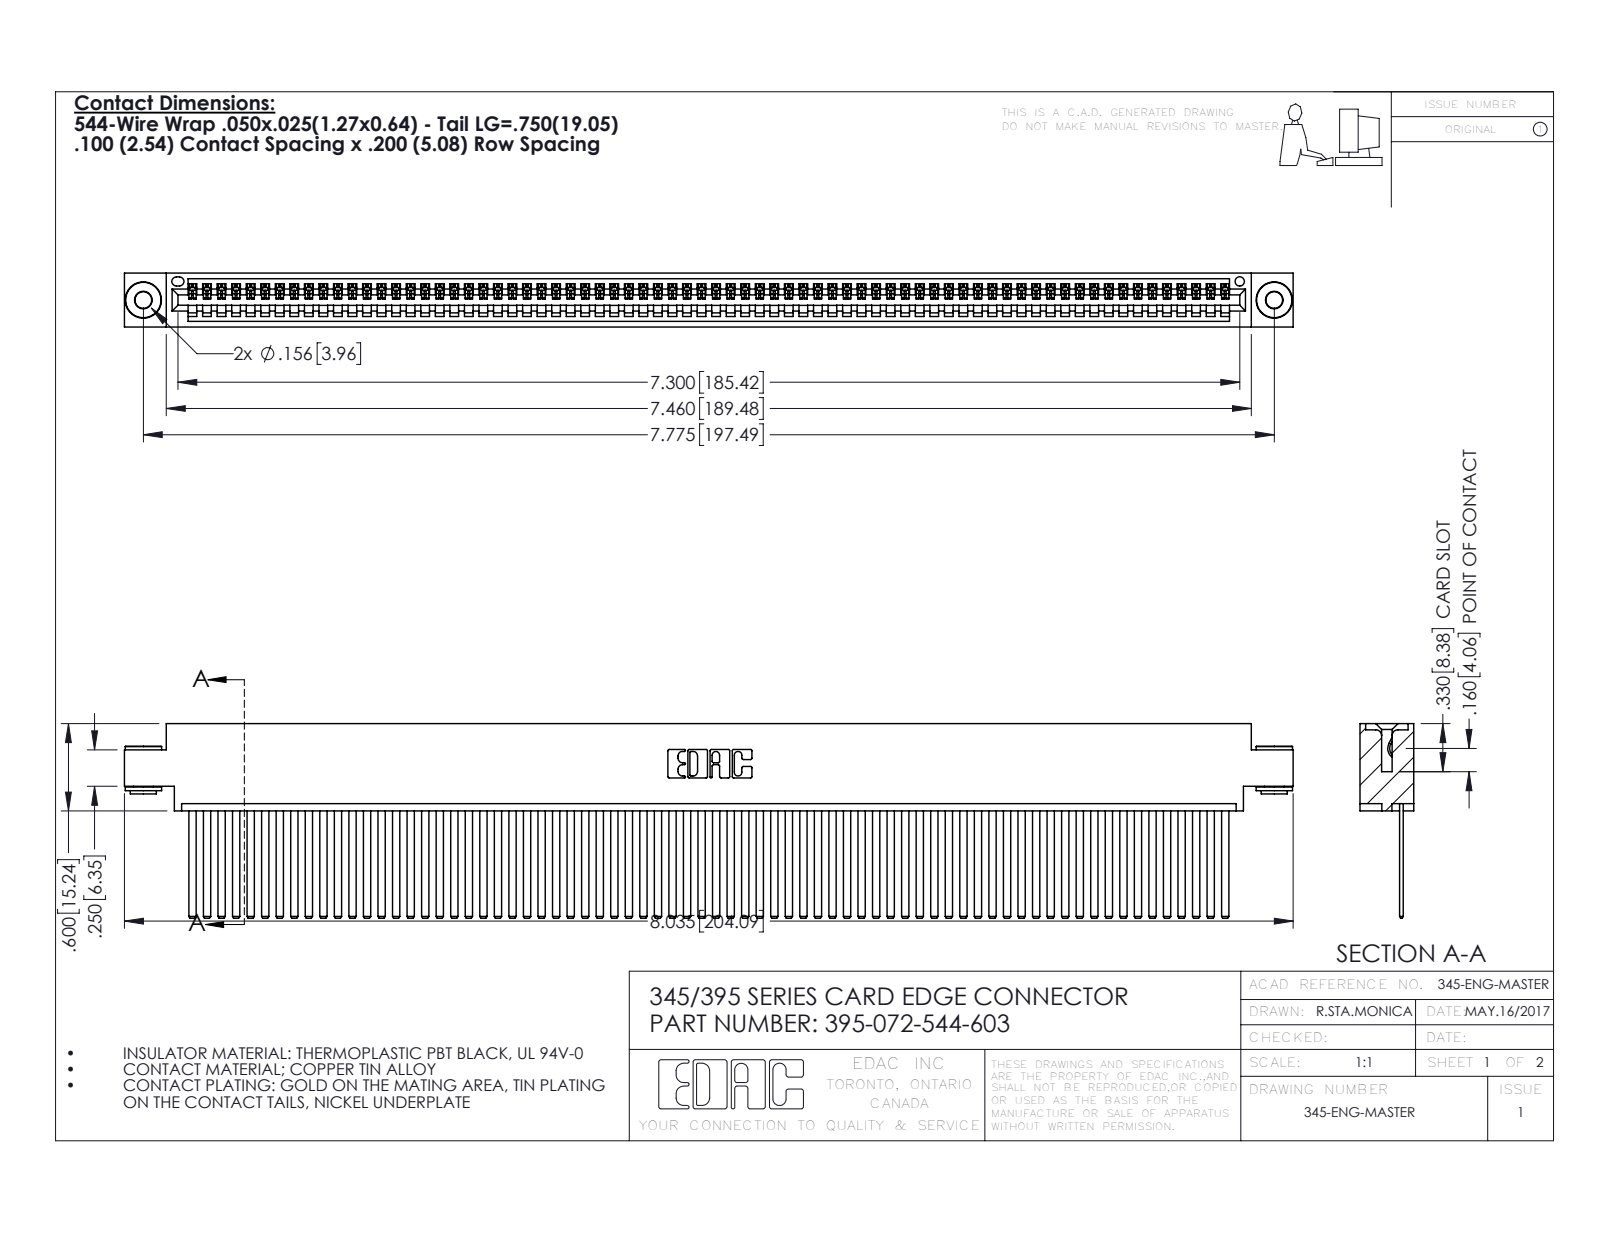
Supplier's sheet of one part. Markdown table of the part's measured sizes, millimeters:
| quantity | value |
| --- | --- |
| part name | 395-072-544-603; 345-292-001_345-293-144; 345-250-002_345-250-002-102; 345 Part_0.170 Offset - 0.156 Dia-TH |
| STEP written by | SolidWorks 2016 (CONFIG_CONTROL_DESIGN) |
| units | millimeters |
| bodies | 75 solids, 3912 faces (2686 planar, 1218 cylindrical, 8 other) |
| overall size | 204.1 × 34 × 9.4 |
| volume | 20 370 mm³ |
| surface area | 30 320 mm² |
| round holes (diameter × count) | 2.9 × 2, 4 × 2, 1.6 × 1 |
| round bosses / shafts (diameter × count) | 6.4 × 2, 4.6 × 2, 3.5 × 2 |
| partial cylindrical surfaces (radius × count) | 0.2 × 144, 0.3 × 22, 0.2 × 6, 0.8 × 6, 0.7 × 3, 0.8 × 2, 1 × 2, 0.4 × 1 |
| main face-to-face distances | 1.8, 7.6, 0.6, 2.5, 6.9, 9.4, 5.1, 5.7, 4.4, 3.8 |
| hole center spacings | 6.9, 191.5, 197.5 |
